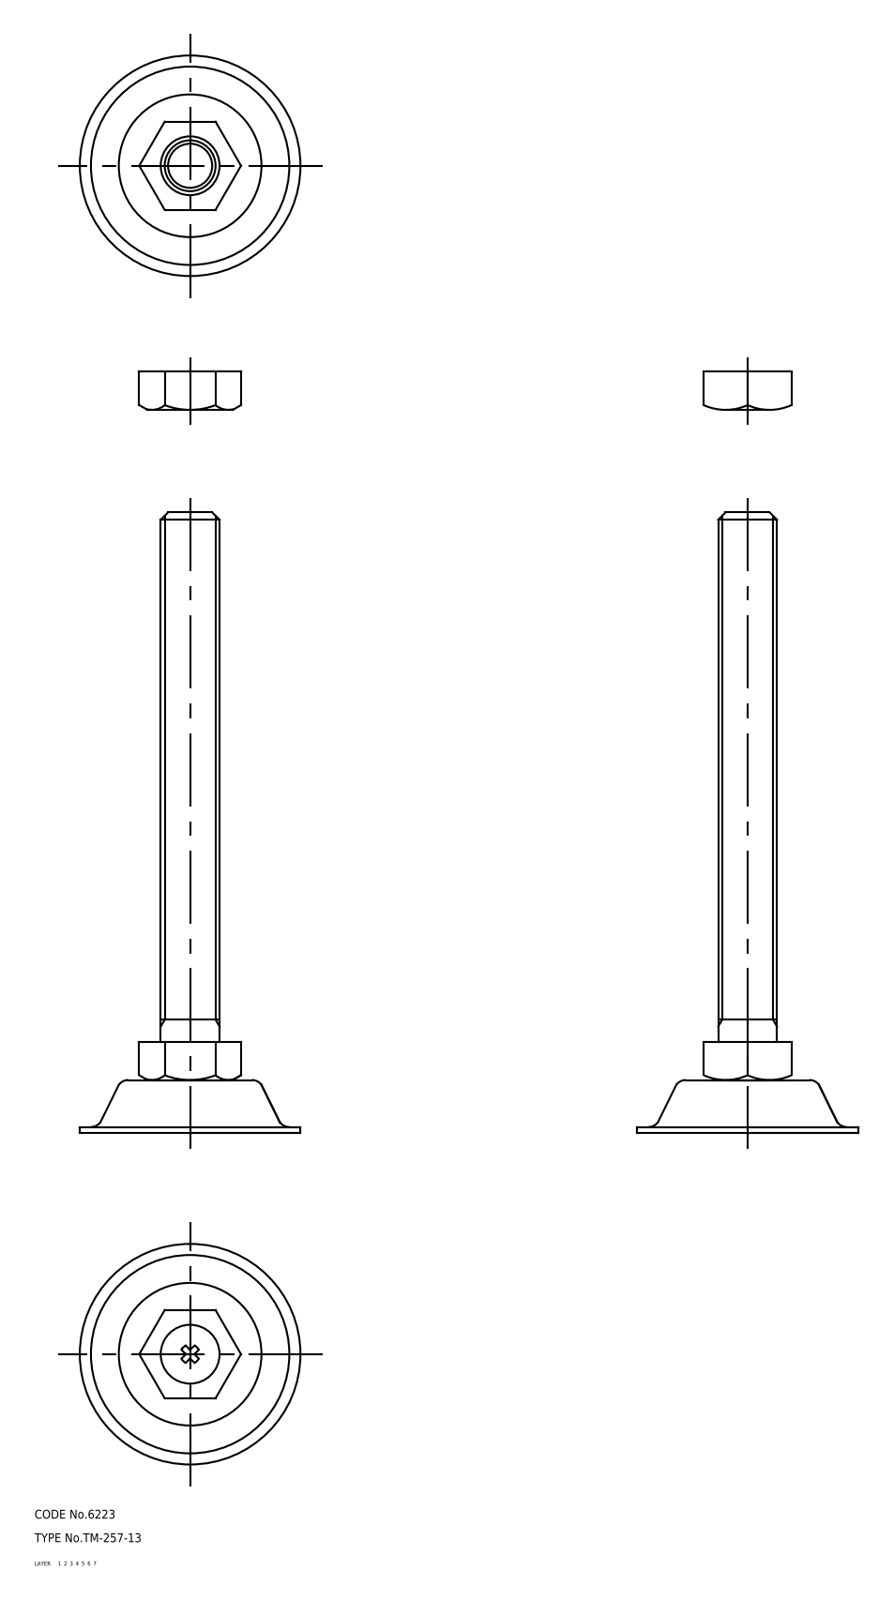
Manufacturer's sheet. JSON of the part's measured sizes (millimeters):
{"part_name": "nut; foot; bolt; TM_257_13_9632_36", "step_written_by": "CADfix (AUTOMOTIVE_DESIGN)", "units": "millimeters", "bodies": {"solids": 4, "faces": 83, "planar": 0, "cylindrical": 0, "other": 83}, "overall_size": [211, 75, 75], "volume_mm3": 94705, "surface_area_mm2": 33066}
